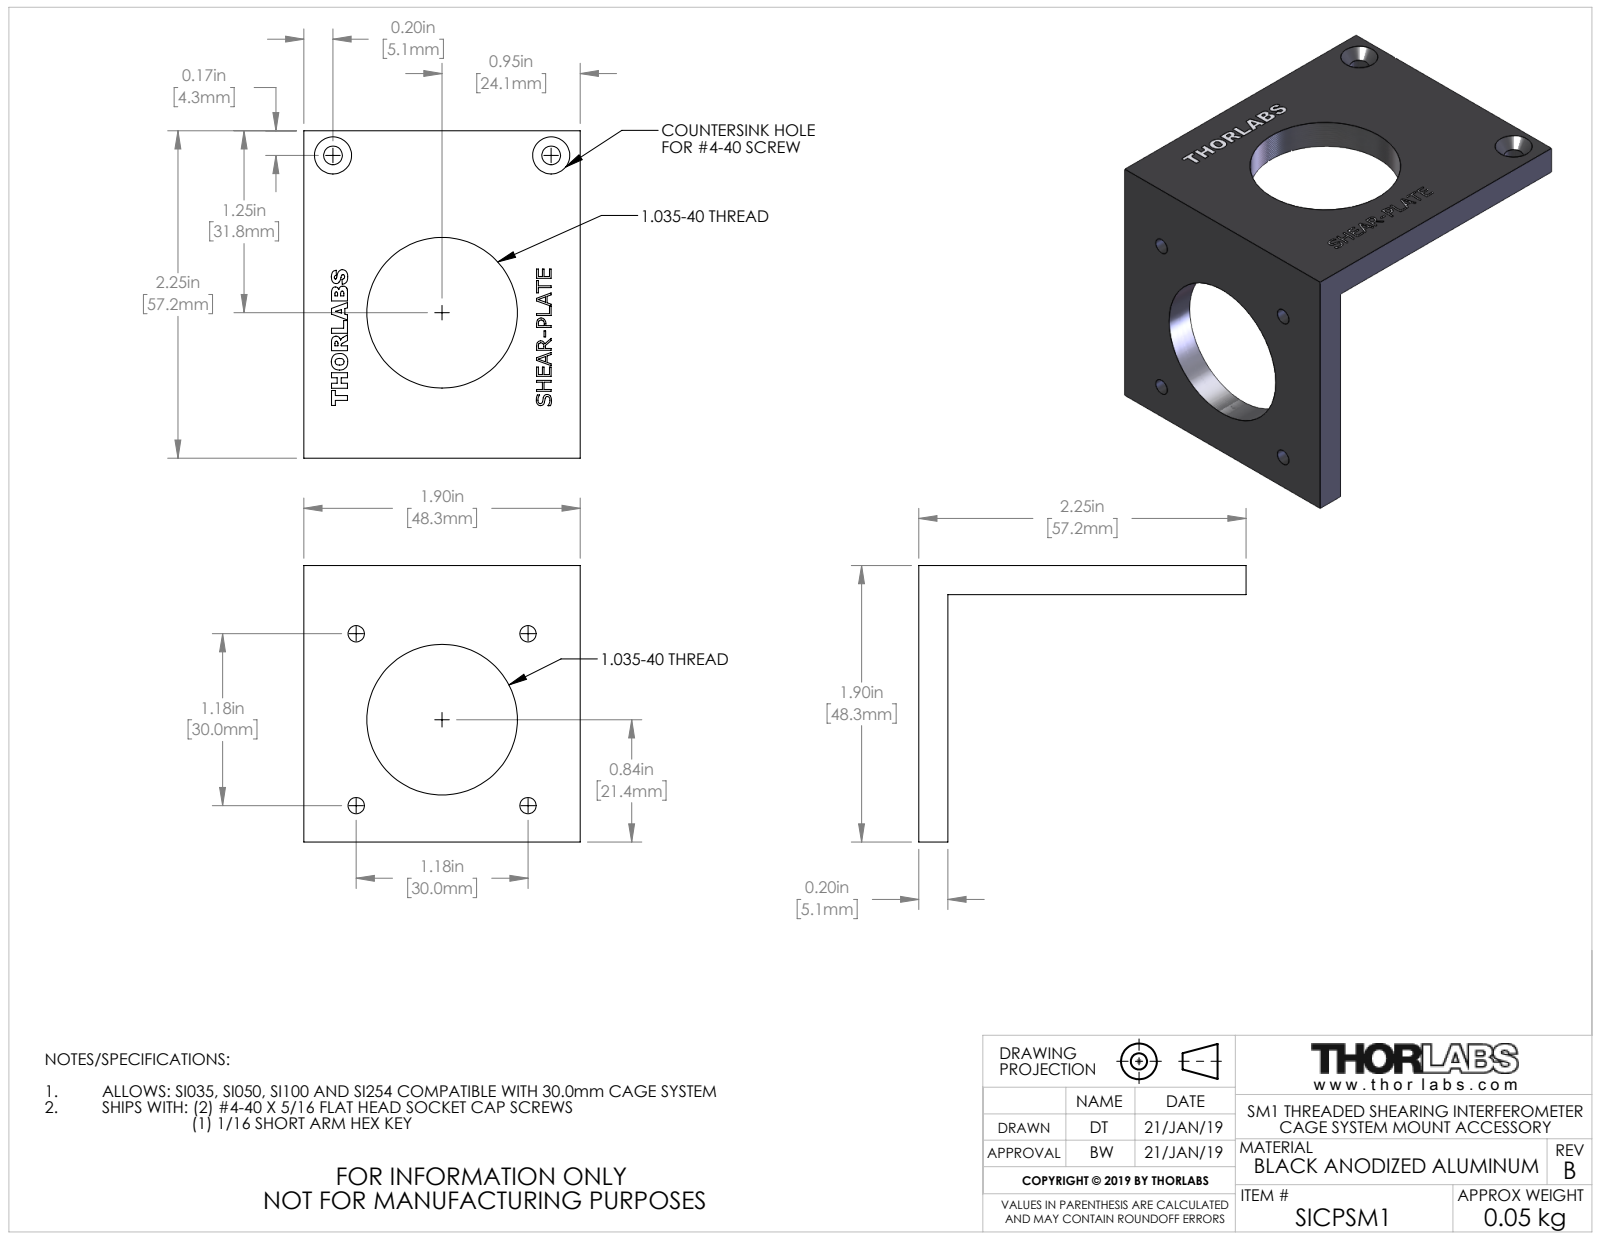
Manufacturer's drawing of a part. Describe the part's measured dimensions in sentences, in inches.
The part is named "TTN015345-E0W". Its 3-D file was written by "SolidWorks 2018 (CONFIG_CONTROL_DESIGN)". It is 1 solid with 56 faces: 36 planar, 16 cylindrical and 4 other. Overall it measures 2.25 by 1.9 by 1.9 inches. Its volume is 1.149 cubic inches and its surface area 15.58 square inches. Round holes: 4 of diameter 0.112, 2 of diameter 0.129, 2 of diameter 1.035. The main face-to-face distances are 0.2, 1.9, 1.7, 2.05, 2.25. The hole center spacings are 0.835, 1.181, 1.316, 1.67, 1.5.
